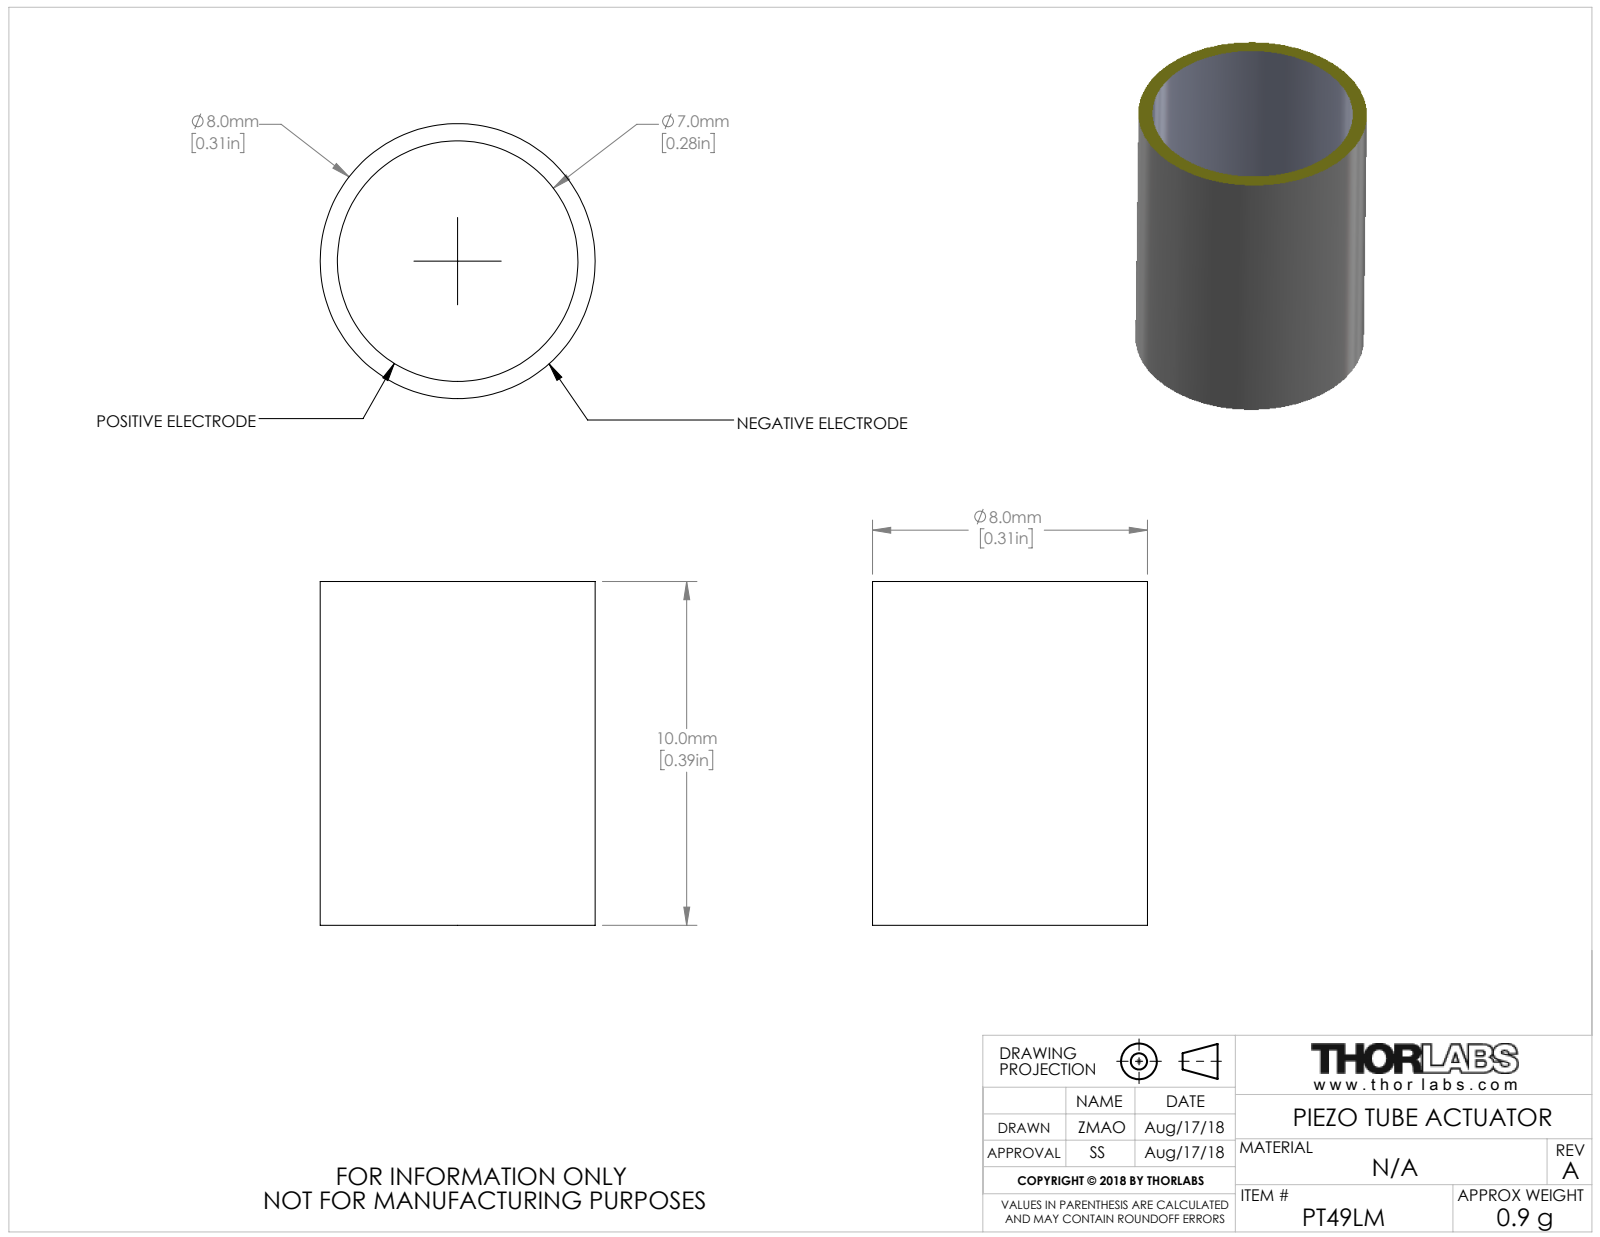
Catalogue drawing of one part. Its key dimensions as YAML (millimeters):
part_name: "CTN011965"
step_written_by: "SolidWorks 2016 (AUTOMOTIVE_DESIGN)"
units: millimeters
bodies: {solids: 1, faces: 6, planar: 2, cylindrical: 4, other: 0}
overall_size: [10, 8, 8]
volume: 118
surface_area: 495
round_holes:
  - {diameter: 7, count: 1}
round_bosses_or_shafts:
  - {diameter: 8, count: 1}
face_to_face_distances: [10]
